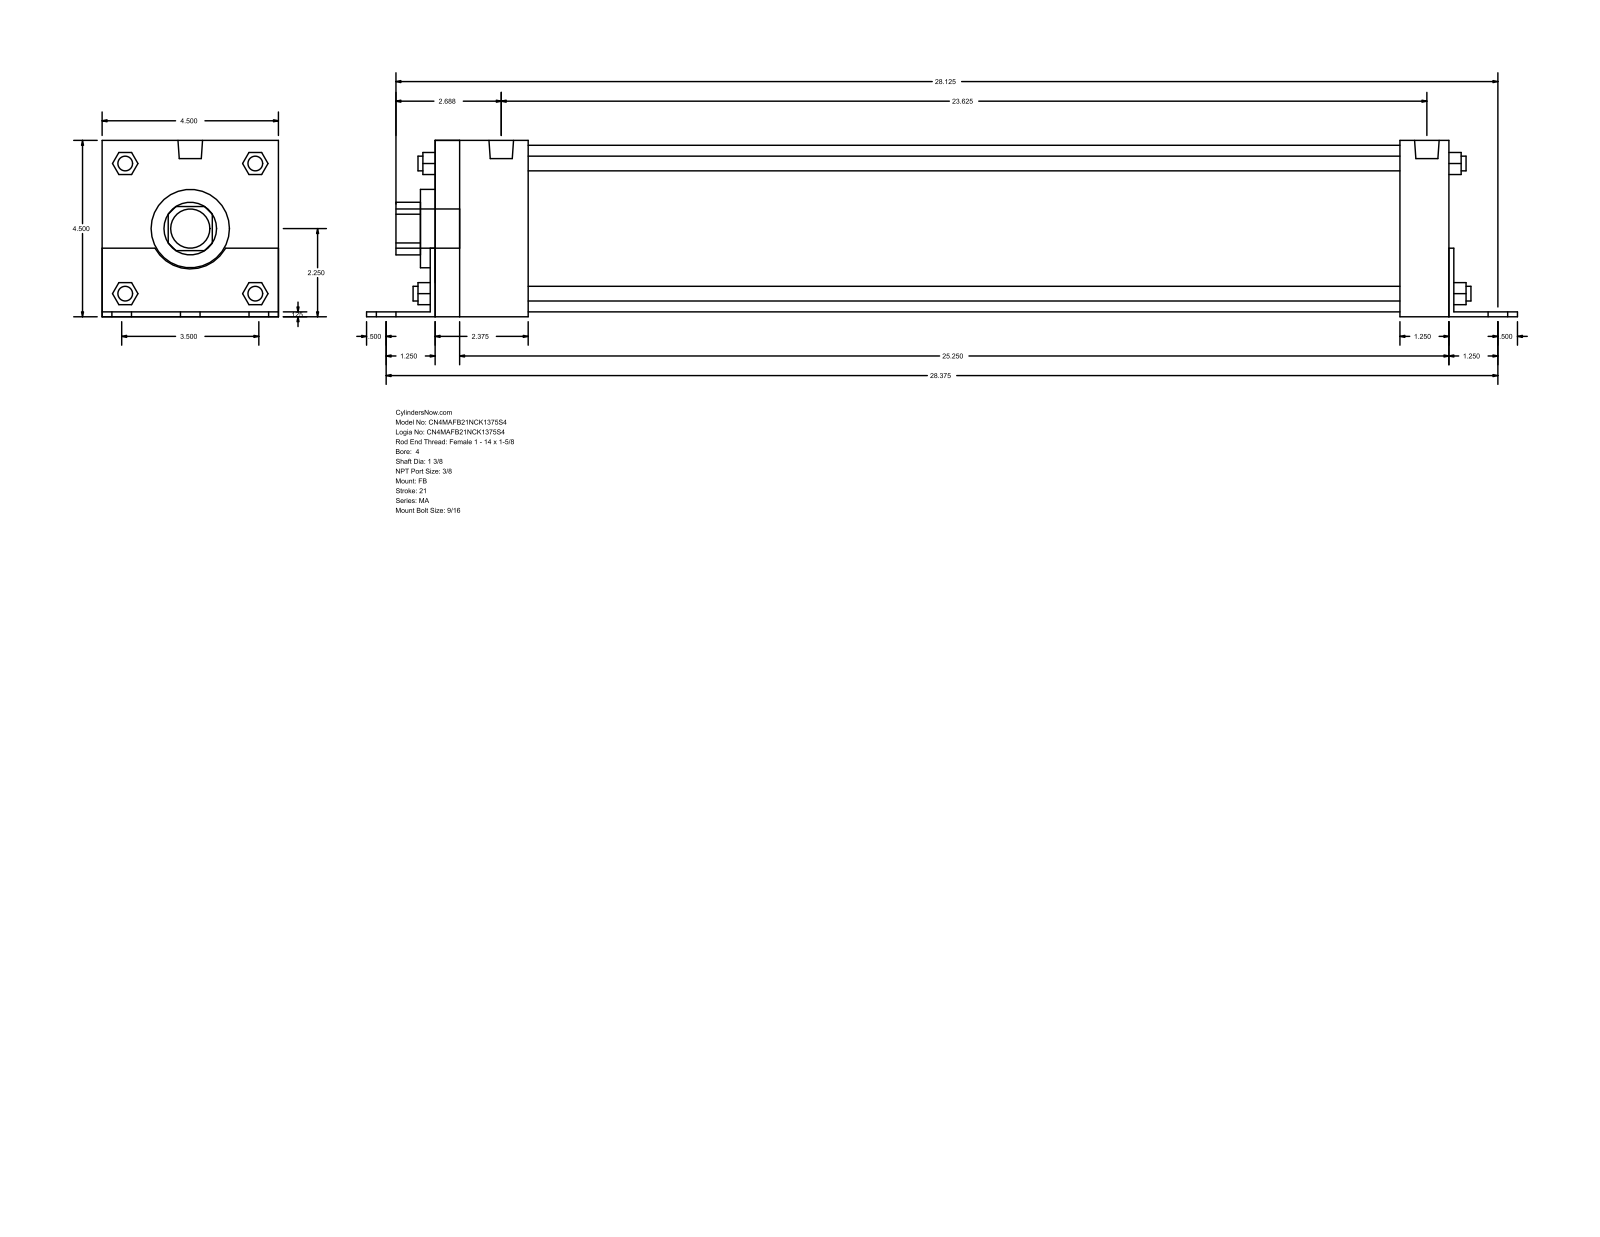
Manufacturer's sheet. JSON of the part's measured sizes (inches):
{"part_name": "MA_FB__0400_1.375", "step_written_by": "GSSL Pune (CONFIG_CONTROL_DESIGN)", "units": "inches", "bodies": {"solids": 0, "faces": 140, "planar": 105, "cylindrical": 35, "other": 0}, "overall_size": [29.375, 4.502, 4.5], "round_holes": [[1.375, 1], [2, 1], [4.25, 1]], "round_bosses_or_shafts": [[0.563, 6], [0.437, 4], [0.375, 4], [0.627, 2], [1, 1]], "partial_cylinders_radius": [[0.672, 1], [1.03, 1]], "face_to_face_distances": [4.5, 0.125, 4.502, 0.123, 4.377, 25.875, 0.125, 26, 2.375, 26]}
